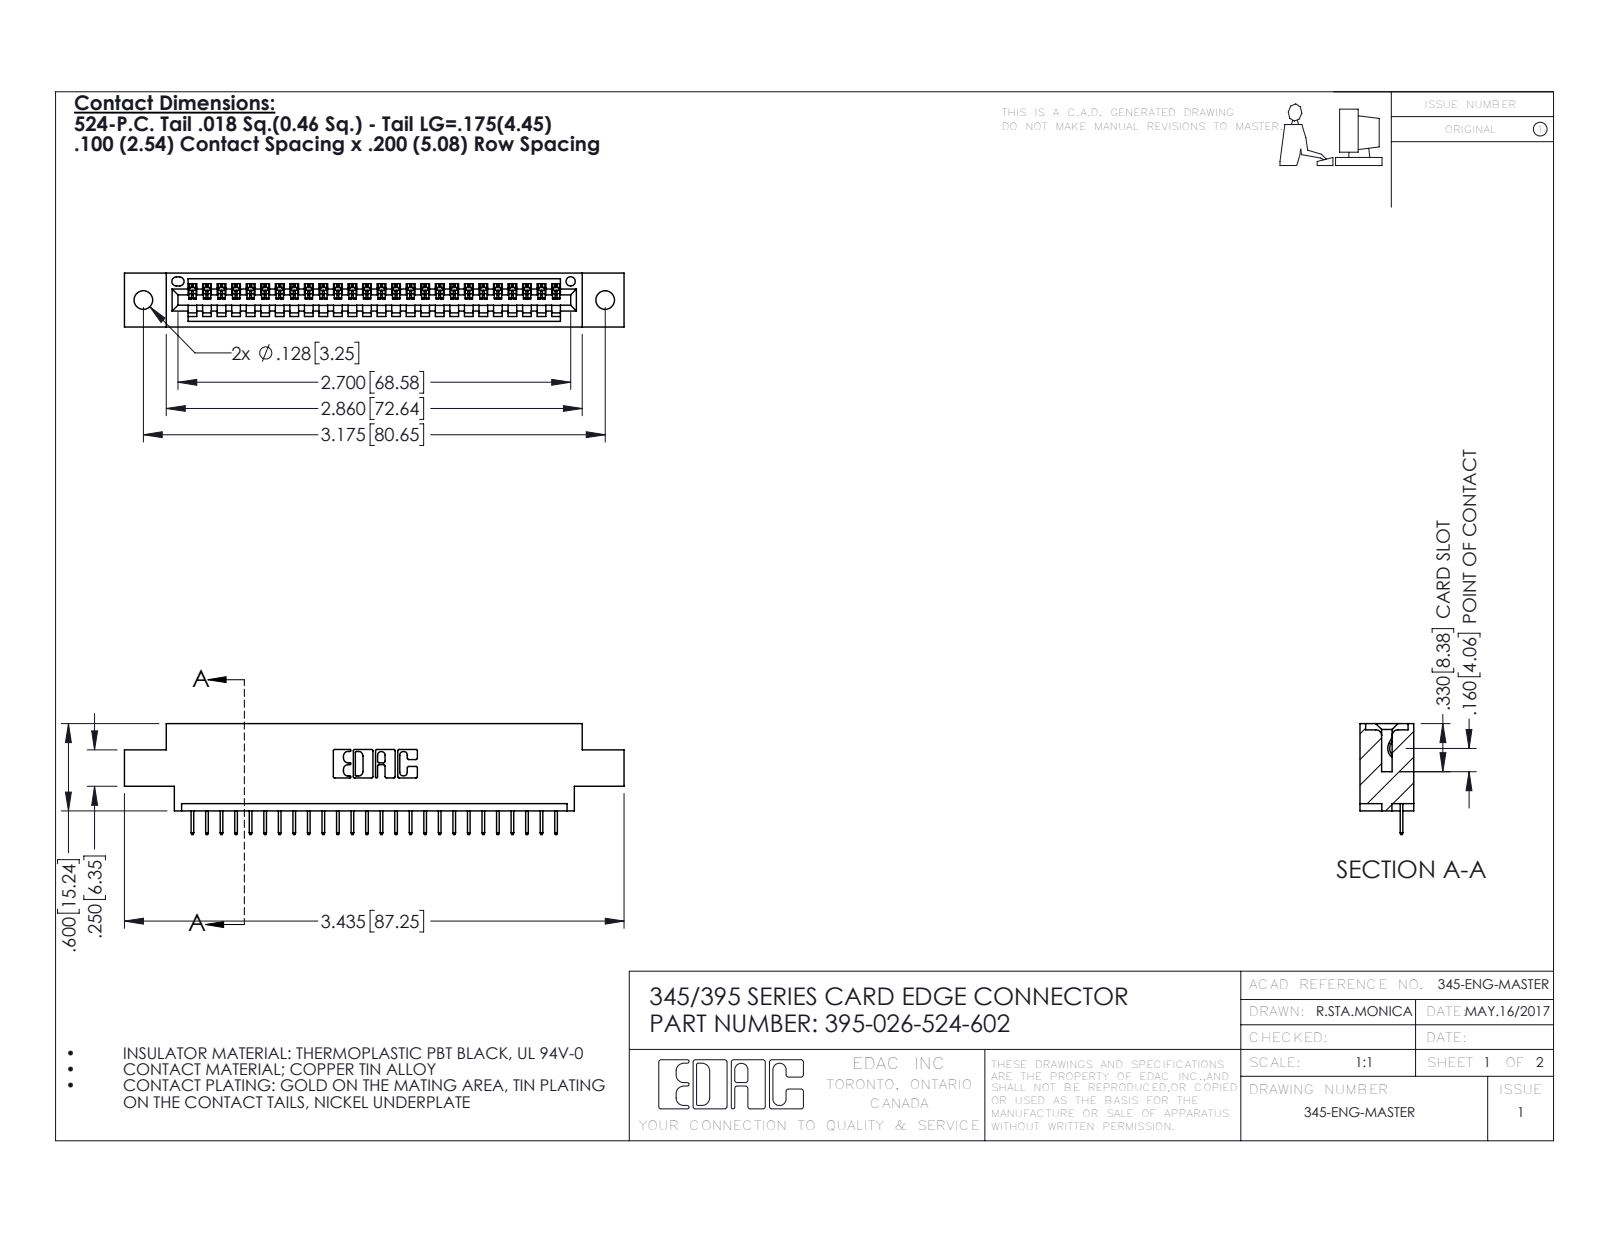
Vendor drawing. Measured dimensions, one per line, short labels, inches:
name: 345 Part_0.170 Offset - 0.128 Dia; 345-292-001_345-293-124; 395-026-524-602
written by: SolidWorks 2016 (CONFIG_CONTROL_DESIGN)
unit: in
bodies: 27 solids, 1742 faces (1280 planar, 462 cylindrical, 0 other)
size: 3.435 × 0.762 × 0.37
volume: 0.482 in³; area: 15.21 in²
holes: 2× ⌀0.128, 1× ⌀0.064
rounds: 52× R0.006, 22× R0.01, 6× R0.007, 6× R0.031, 3× R0.026, 2× R0.031, 2× R0.04, 1× R0.014
face distances: 0.072, 0.298, 0.37, 0.2, 0.098, 0.272, 0.025, 0.225, 0.072, 0.175
hole spacings: 0.27, 2.94, 3.175
